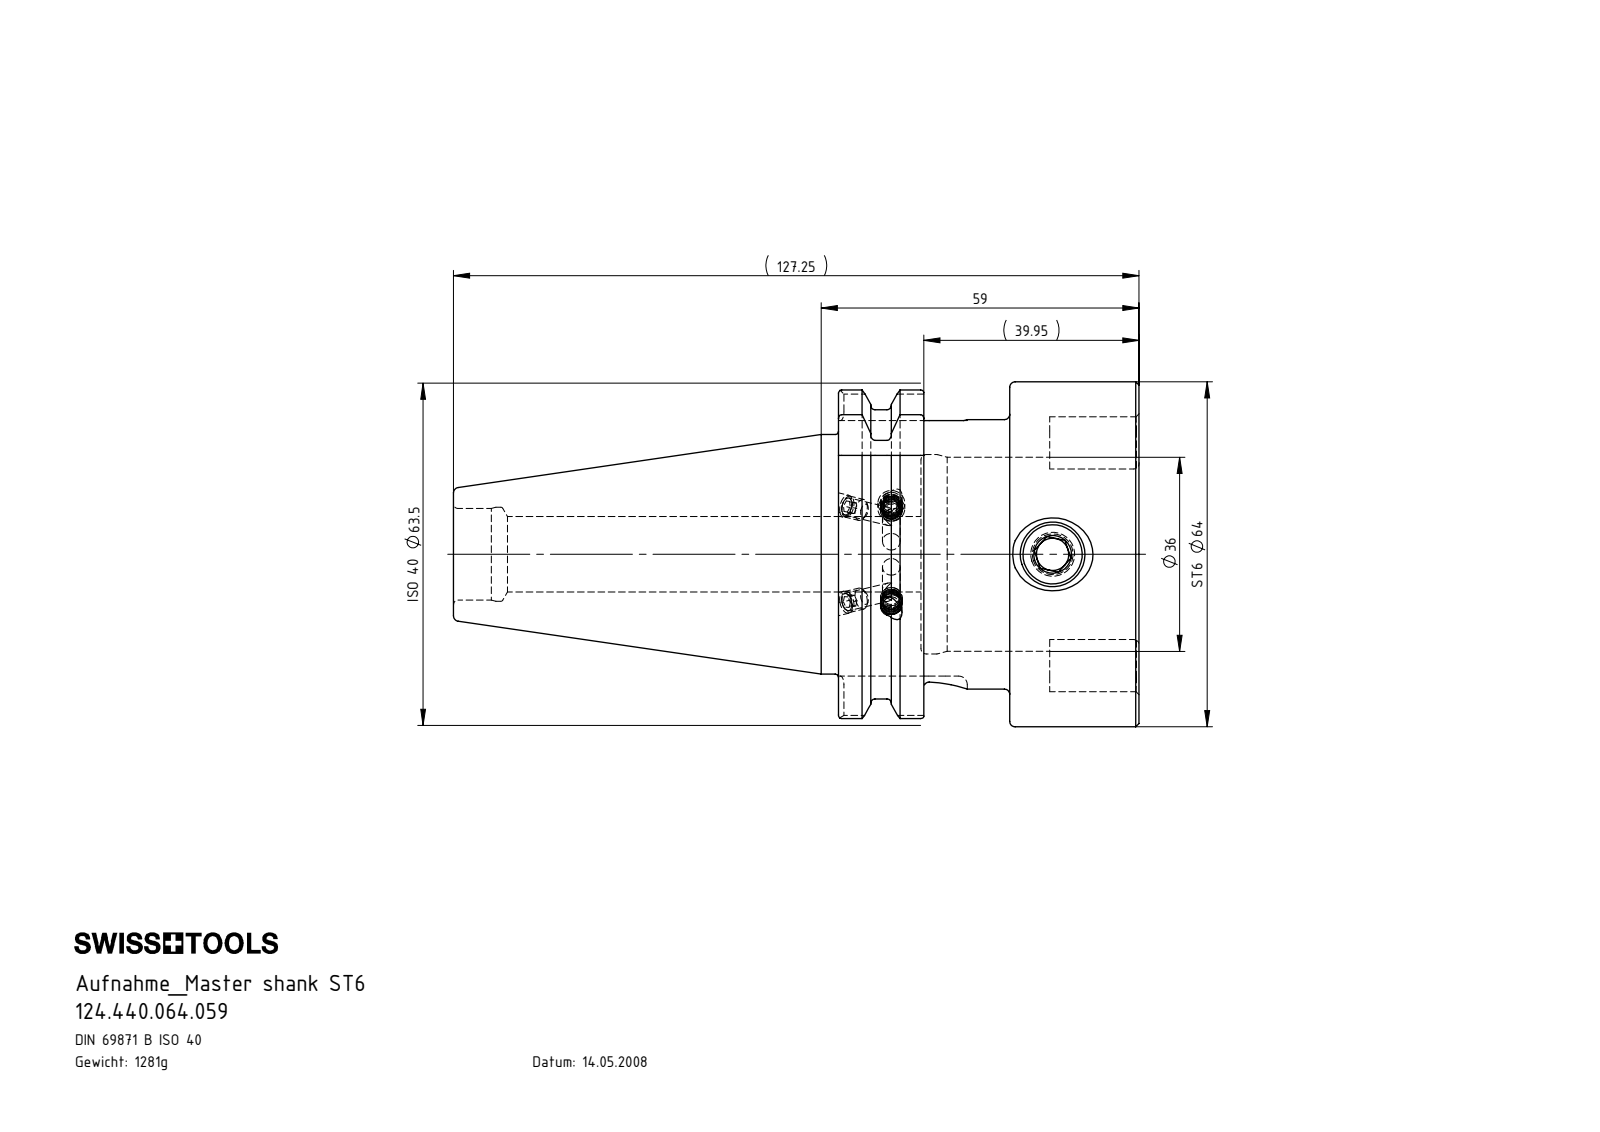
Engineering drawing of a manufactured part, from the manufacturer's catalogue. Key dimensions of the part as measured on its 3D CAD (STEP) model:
Part name (STEP PRODUCT): KVT_MB_600_040; SB4-ST6.K01.059_C_mit Bundkhlung; SB4.ST6.K01.059; ISO 4026 - M4 x 4_PreviewCfg (+2 more)
STEP written by: SolidWorks 2017 (AUTOMOTIVE_DESIGN)
Units: millimetres
Bodies: 9 solids, 235 faces (90 planar, 56 cylindrical, 89 other)
Overall size (bounding box): 127.25 × 64 × 64
Volume: 163 191 mm³ · Surface area: 36 940 mm²
Round holes (diameter × count): ⌀3.3 ×3, ⌀3 ×2, ⌀4.2 ×2, ⌀4 ×1, ⌀6 ×1, ⌀11 ×1, ⌀14 ×1, ⌀17 ×1, ⌀17.45 ×1, ⌀36 ×1, ⌀37 ×1
Round bosses / shafts (diameter × count): ⌀4 ×4, ⌀64 ×1, ⌀50 ×1, ⌀44.45 ×1, ⌀12 ×1, ⌀5 ×1
Partial cylindrical surfaces — rounded edges, fillets, slot ends (radius × count): R1.6 ×8, R5.2 ×2, R8 ×1, R8.05 ×1, R28 ×1, R31.75 ×1
Main face-to-face distances: 55.8, 31.8, 24, 15.3, 16.5, 40.5, 15.95, 15.85, 0.55, 39.95
